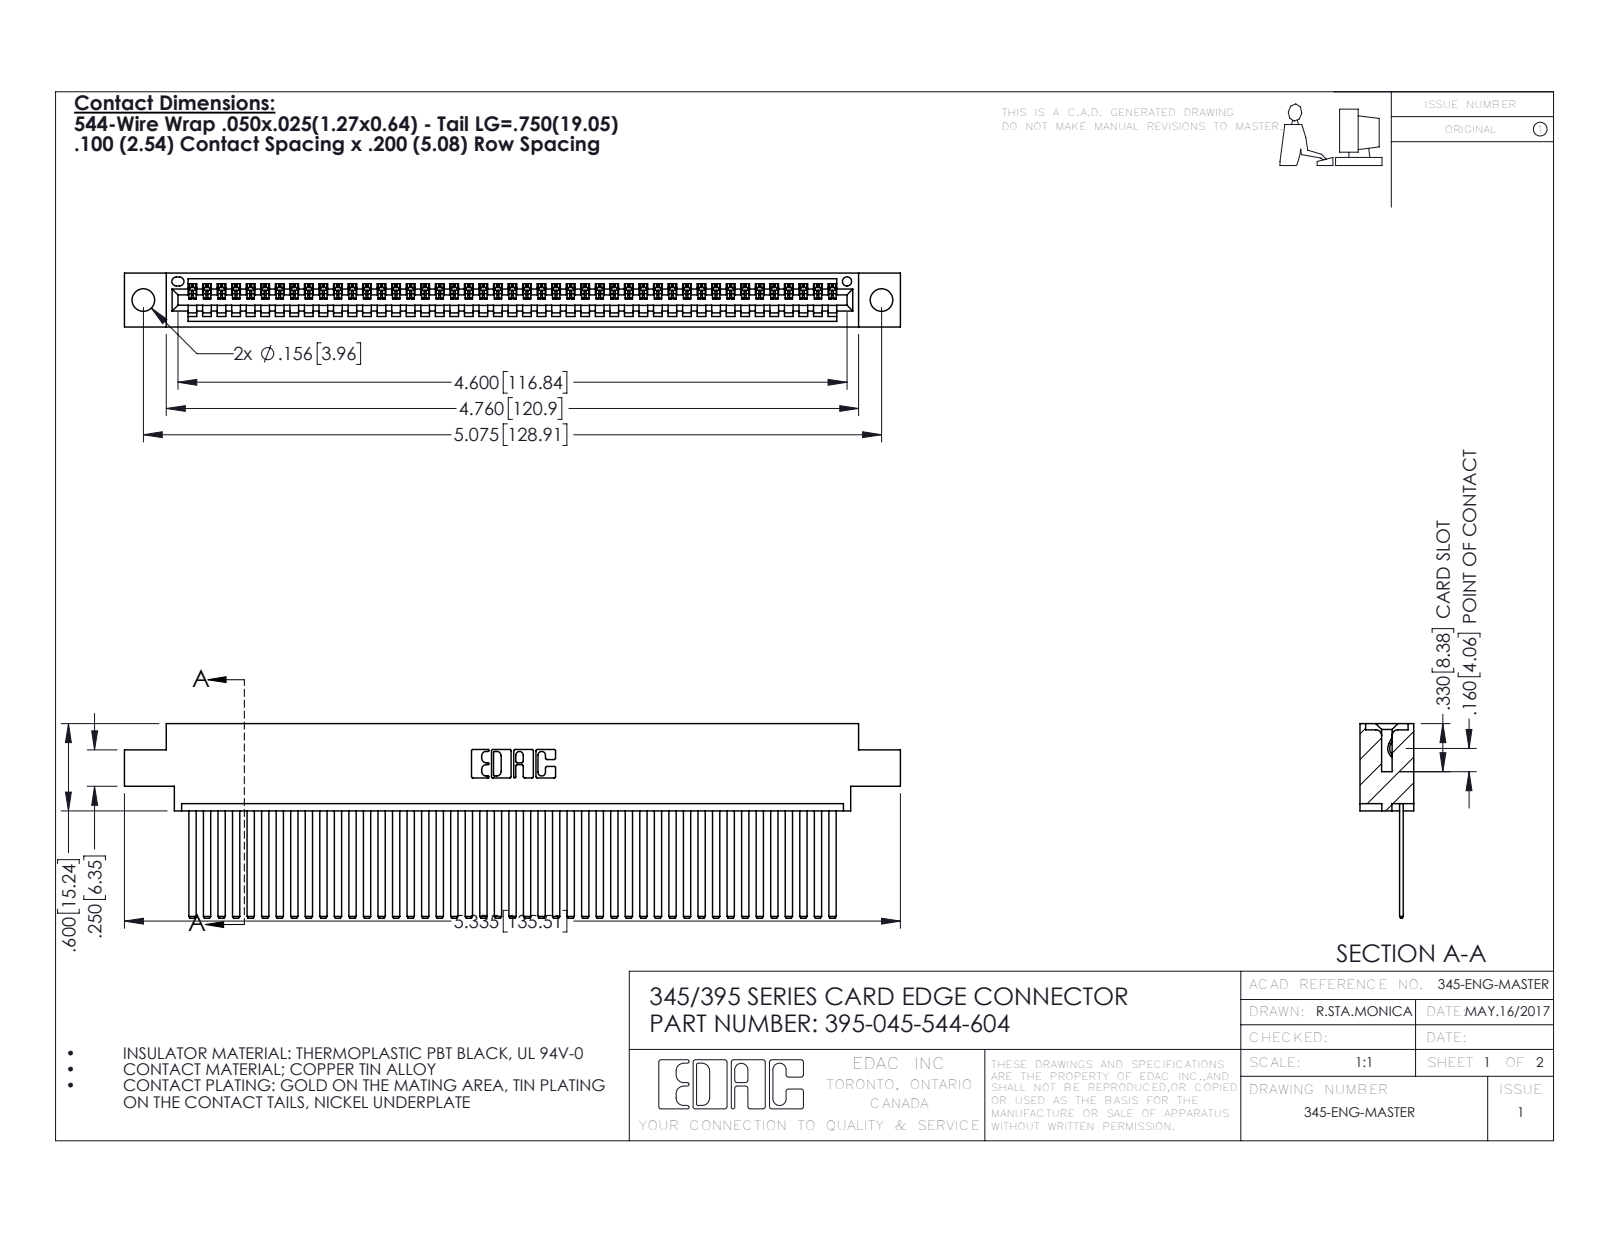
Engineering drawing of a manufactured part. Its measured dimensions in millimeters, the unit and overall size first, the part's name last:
Units: millimetres
Overall size (bounding box): 135.5 × 34 × 9.4
Round holes (diameter × count): ⌀4 ×2, ⌀1.6 ×1
Partial cylindrical surfaces — rounded edges, fillets, slot ends (radius × count): R0.2 ×90, R0.3 ×22, R0.2 ×6, R0.8 ×6, R0.7 ×3, R0.8 ×2, R1 ×2, R0.4 ×1
Main face-to-face distances: 1.8, 7.6, 0.6, 2.5, 6.9, 9.4, 5.1, 5.7, 4.4, 3.8
Hole centre spacings: 6.9, 122.9, 128.9
Volume: 13 200 mm³ · Surface area: 19 100 mm²
Bodies: 46 solids, 2470 faces (1704 planar, 766 cylindrical, 0 other)
Part name (STEP PRODUCT): 395-045-544-604; 345 Part_0.170 Offset - 0.156 Dia-TH; 345-292-001_345-293-144
STEP written by: SolidWorks 2016 (CONFIG_CONTROL_DESIGN)
